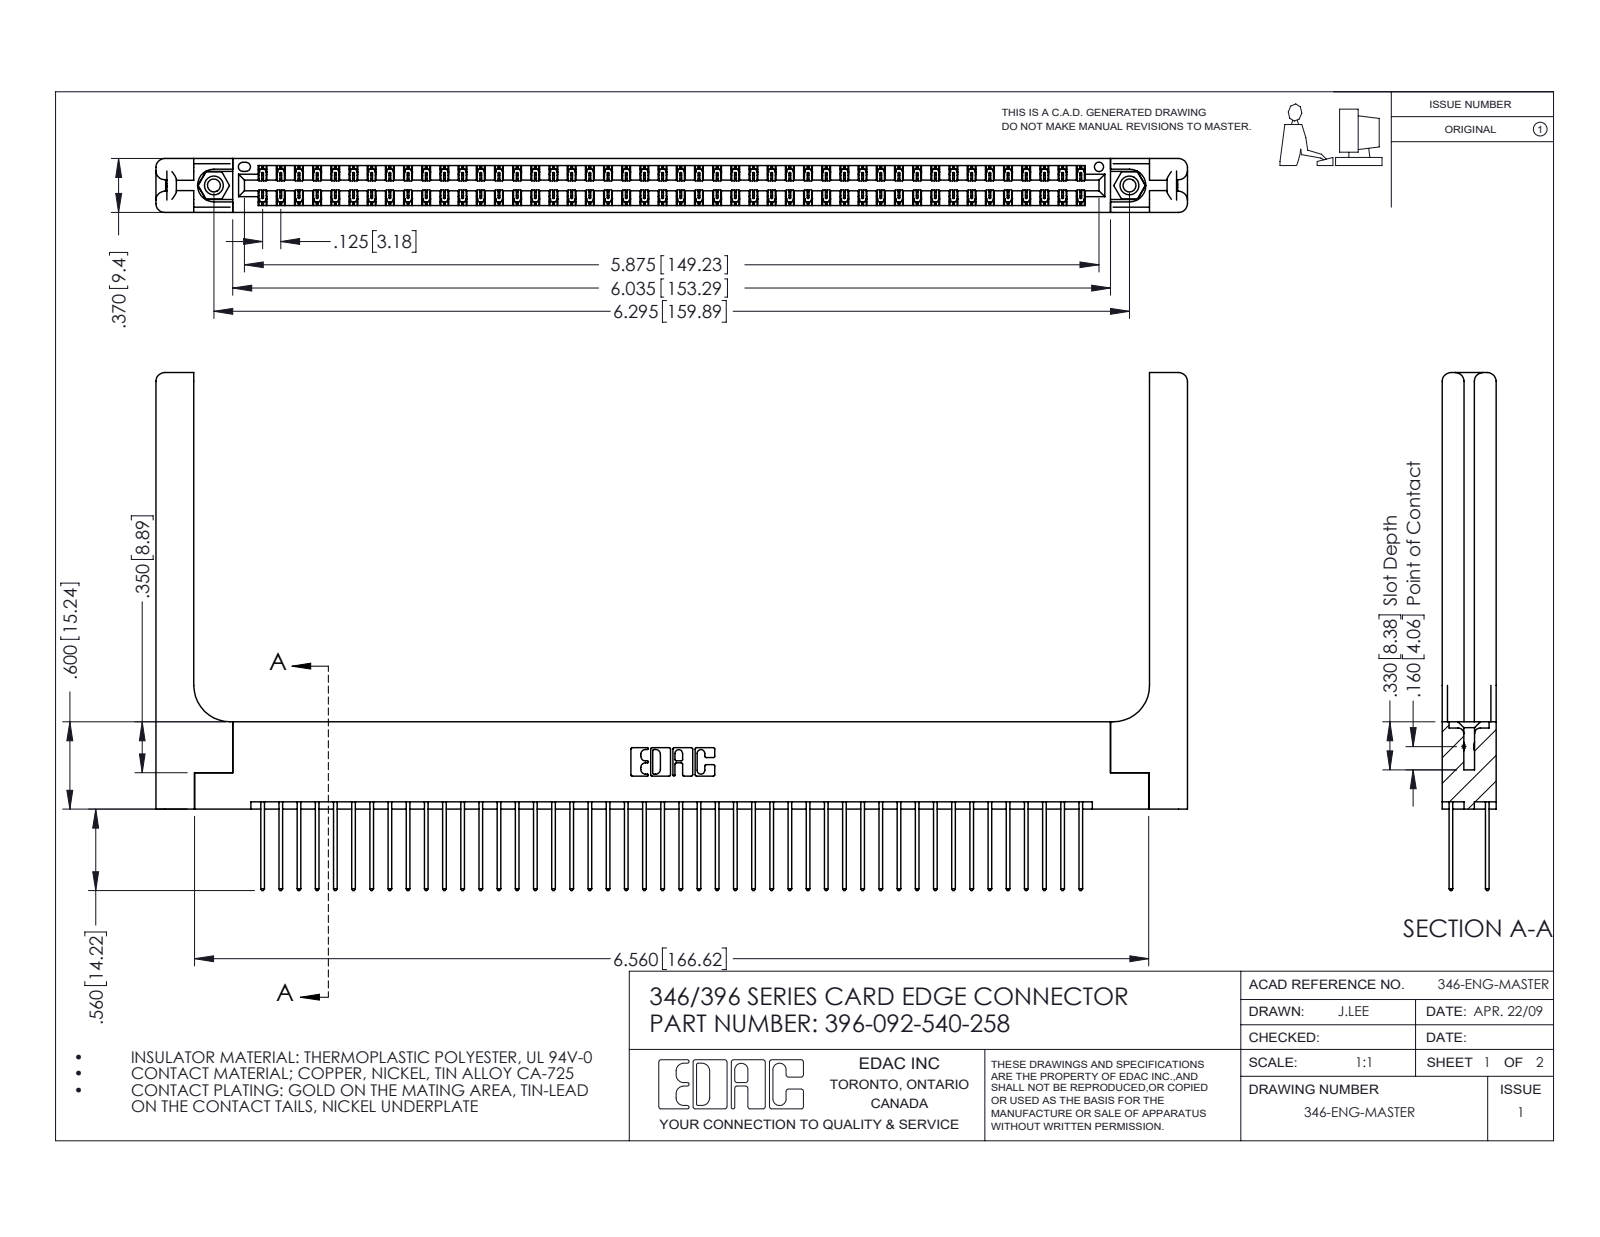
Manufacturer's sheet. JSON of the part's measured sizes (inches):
{"part_name": "345-292-001_345-293-140; 346-220-058_345-220-058; 345-250-001_345-250-001-102; 346 Part_Flush Mounting Lugs - 0.156 Dia-TH (+1 more)", "step_written_by": "SolidWorks 2016 (CONFIG_CONTROL_DESIGN)", "units": "inches", "bodies": {"solids": 97, "faces": 5162, "planar": 3444, "cylindrical": 1658, "other": 60}, "overall_size": [7.091, 3.56, 0.37], "volume_in3": 1.552, "surface_area_in2": 48.59, "round_holes": [[0.089, 2], [0.125, 2], [0.156, 2], [0.064, 1]], "round_bosses_or_shafts": [[0.155, 2]], "partial_cylinders_radius": [[0.006, 138], [0.01, 92], [0.01, 22], [0.06, 16], [0.007, 6], [0.031, 6], [0.026, 3], [0.014, 2]], "face_to_face_distances": [0.048, 0.322, 0.072, 0.37, 0.25, 0.025, 0.298, 0.148, 0.15, 0.275], "hole_center_spacings": [0.246, 6.086, 6.295]}
